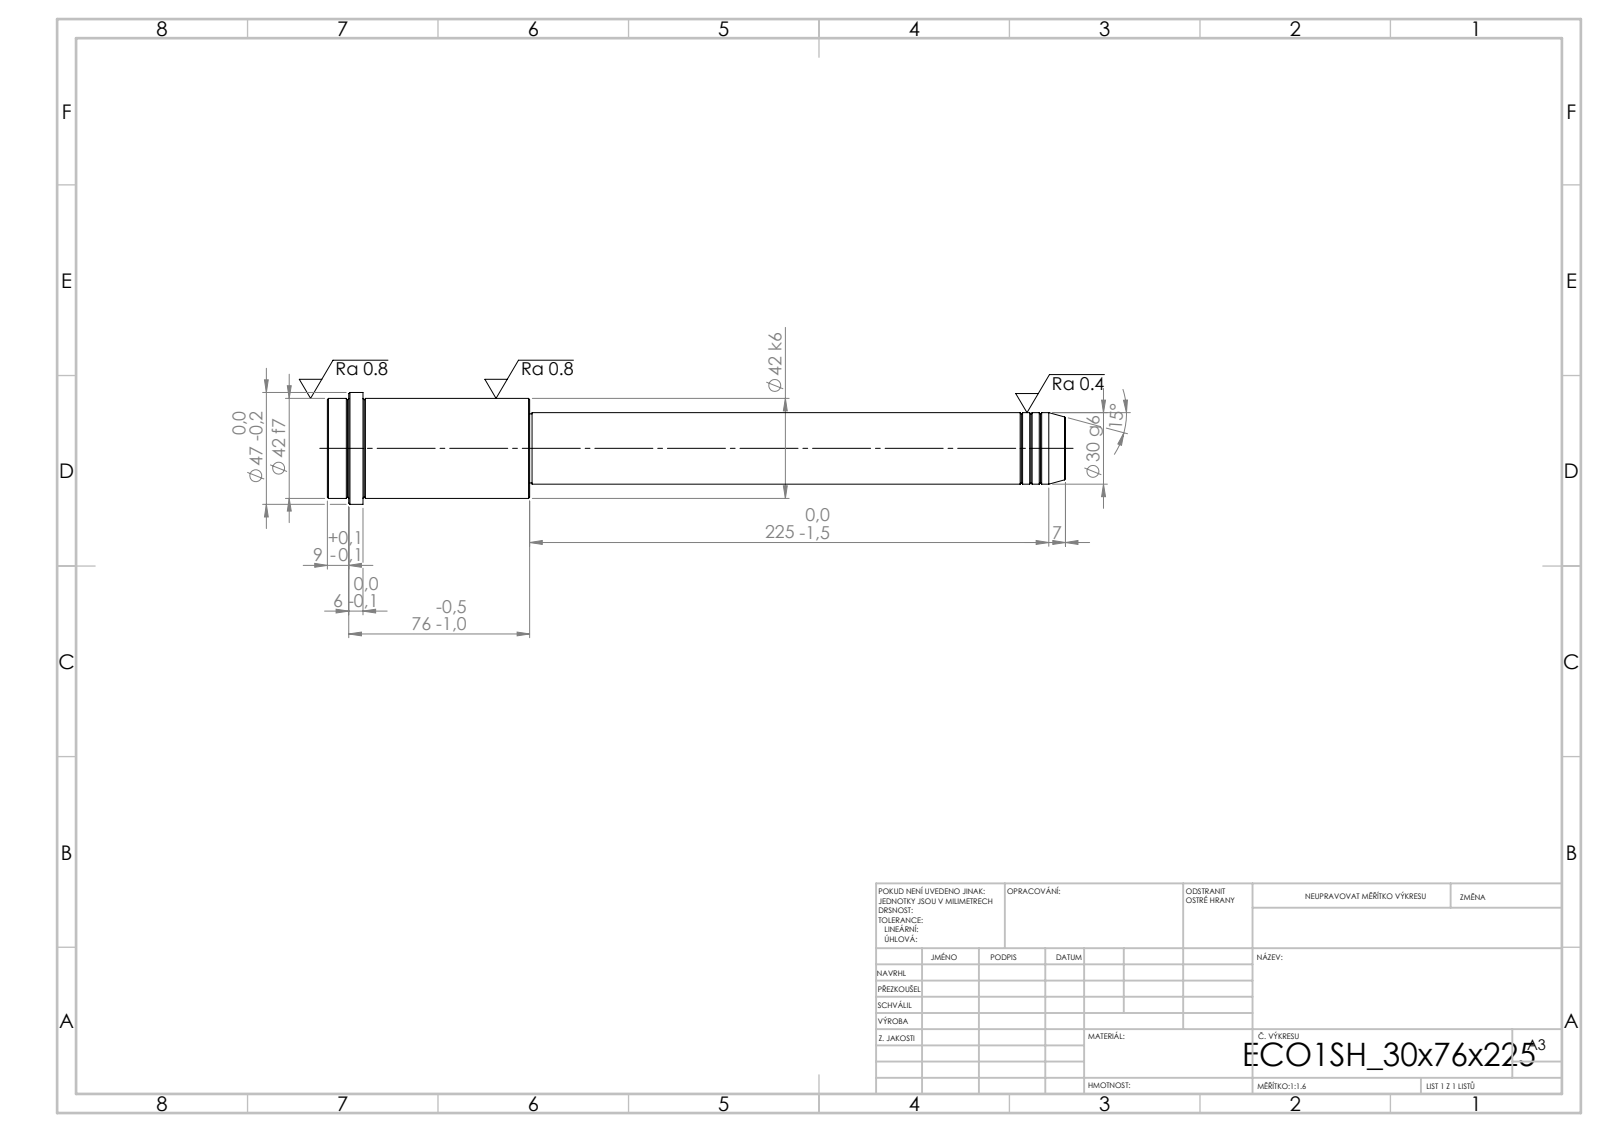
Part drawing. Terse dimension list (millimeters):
written by: SolidWorks 2019 (CONFIG_CONTROL_DESIGN)
unit: mm
bodies: 1 solid, 52 faces (6 planar, 16 cylindrical, 30 other)
size: 310 × 47 × 47
volume: 277 998 mm³; area: 36 055 mm²
bosses: 1× ⌀47, 1× ⌀42, 1× ⌀30, 1× ⌀29
face distances: 85, 225, 310, 295, 70, 15, 301, 76, 6, 9
